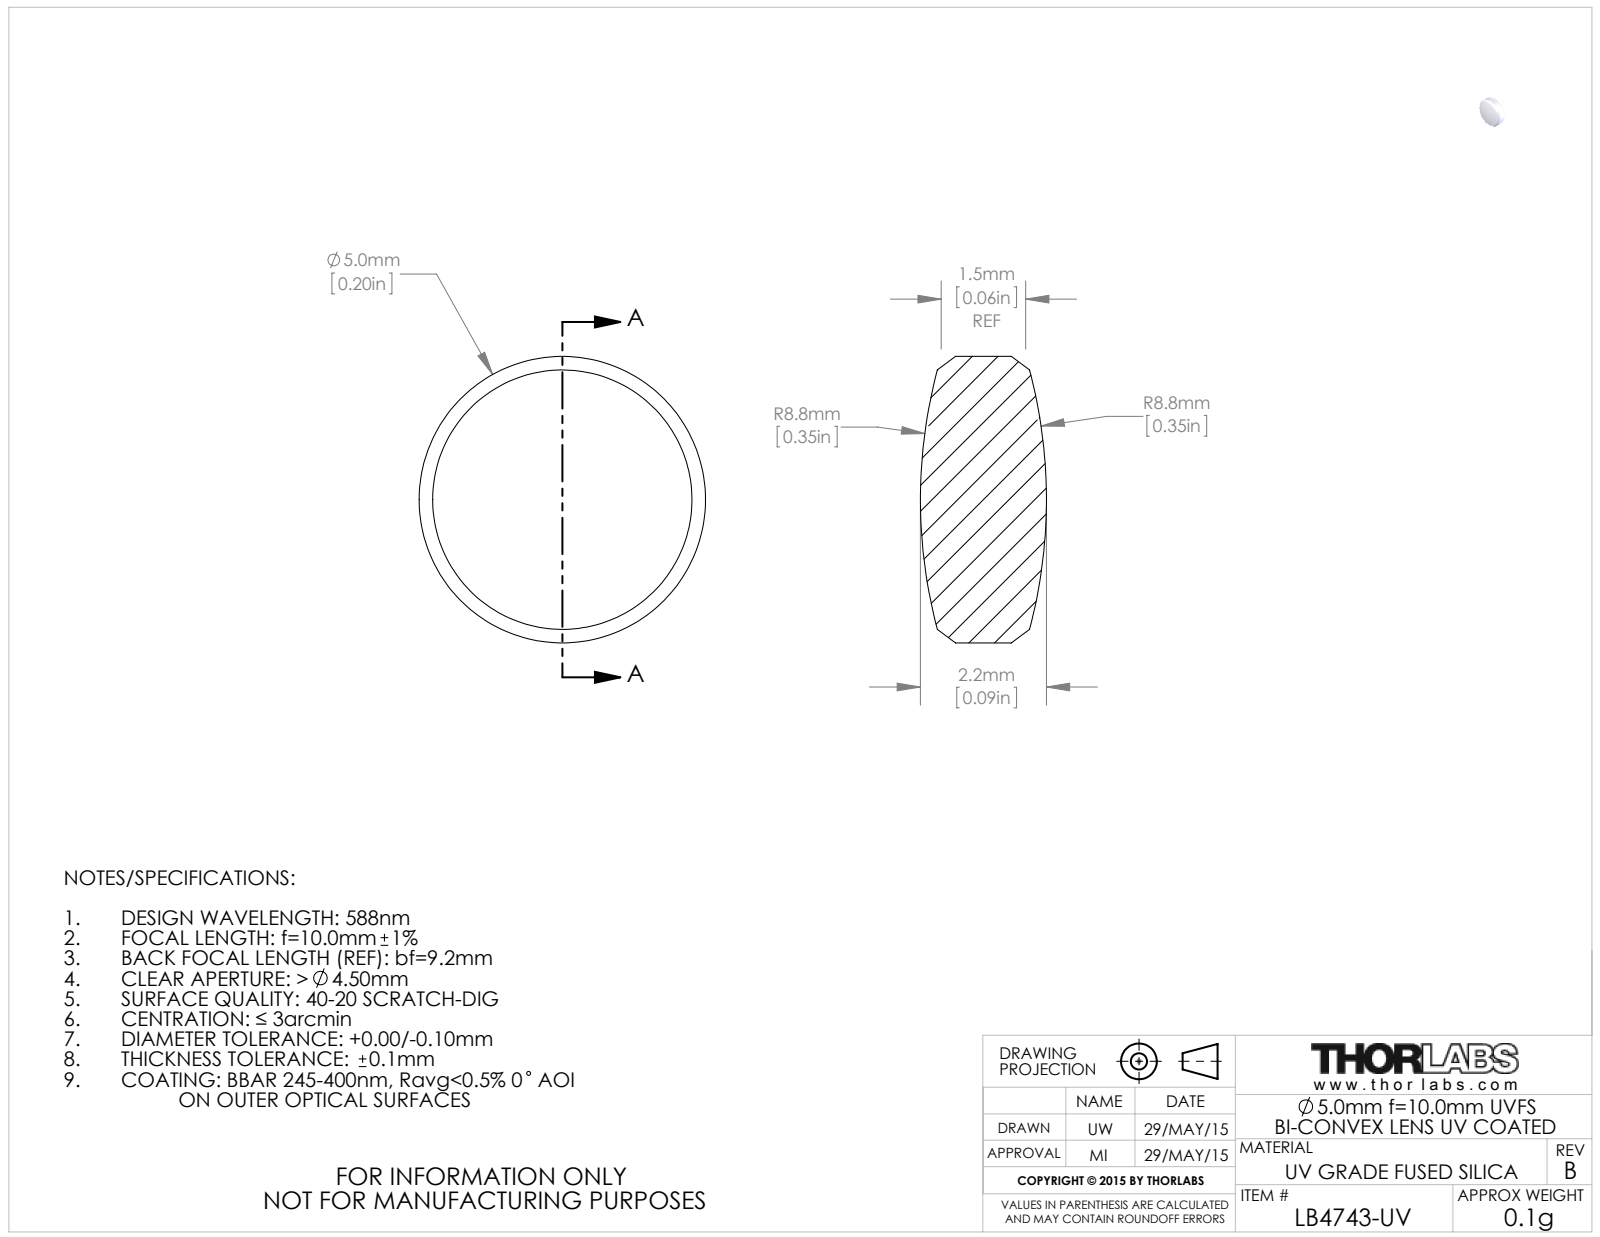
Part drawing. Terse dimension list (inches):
name: 4306-E0W
written by: SolidWorks 2014 (CONFIG_CONTROL_DESIGN)
unit: in
bodies: 1 solid, 10 faces (0 planar, 2 cylindrical, 8 other)
size: 0.197 × 0.197 × 0.087
volume: 0.002 in³; area: 0.093 in²
bosses: 1× ⌀0.197
